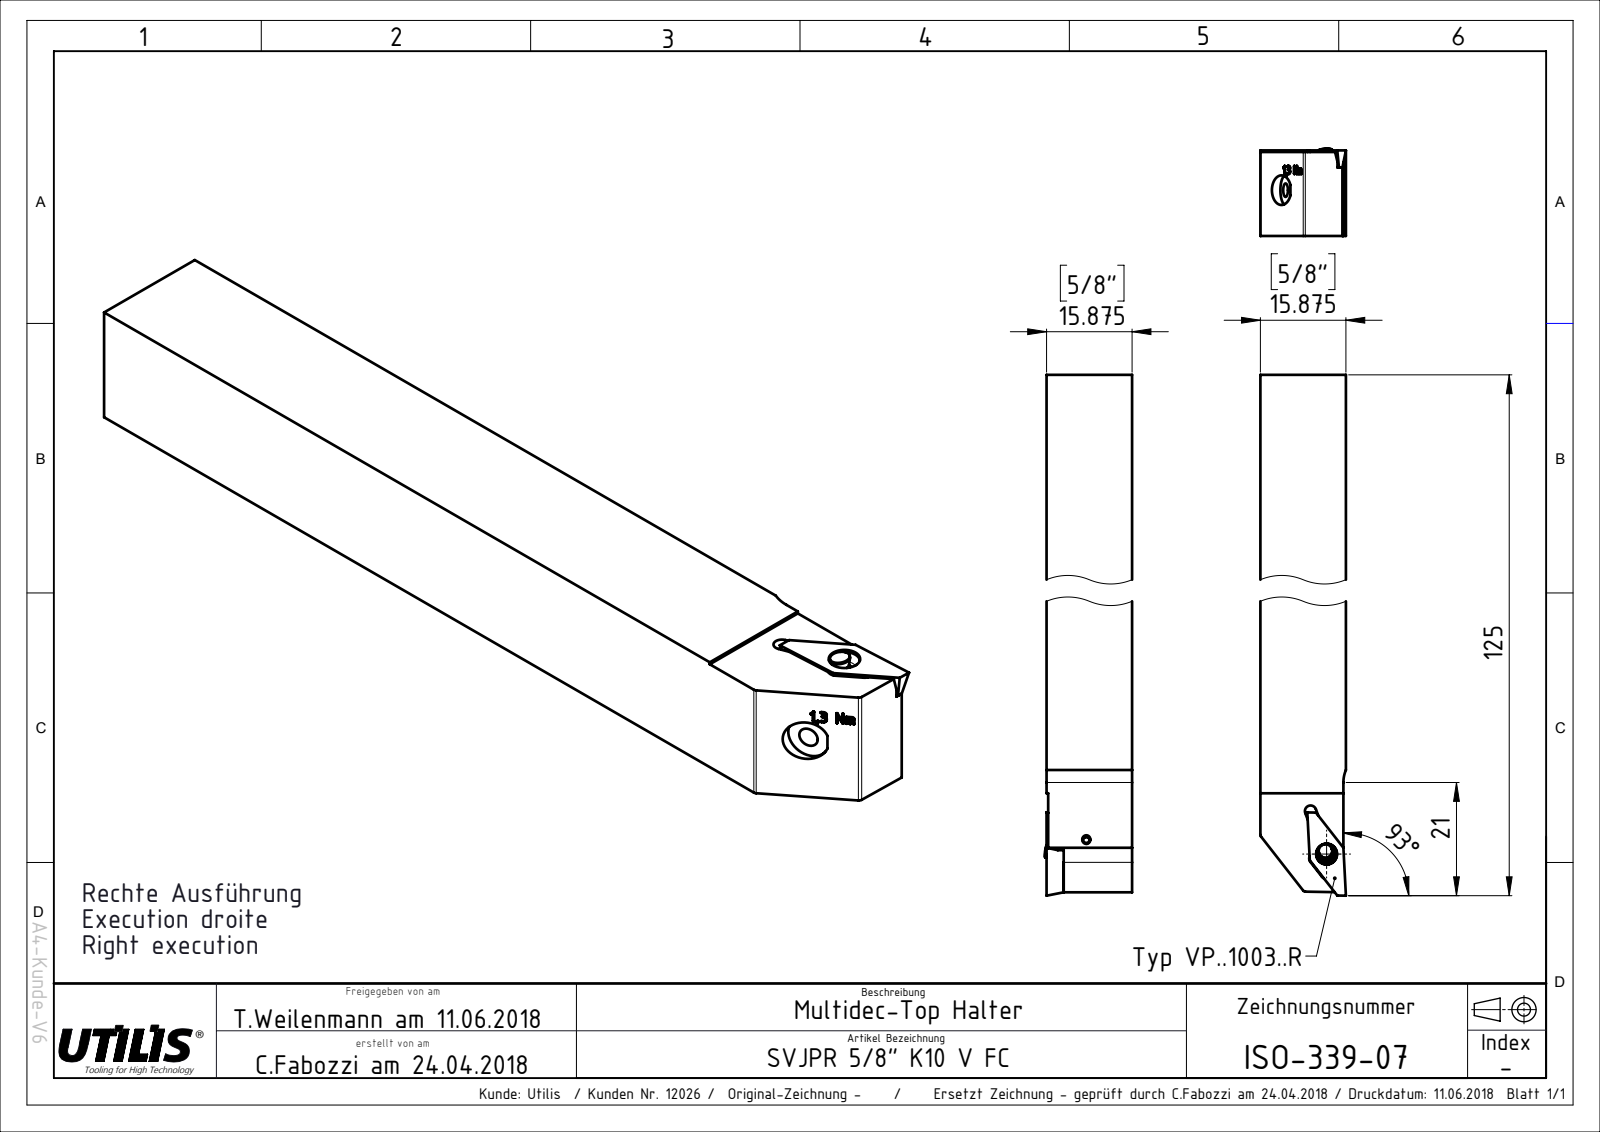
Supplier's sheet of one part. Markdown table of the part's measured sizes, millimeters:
| quantity | value |
| --- | --- |
| part name | ISO-339-07 |
| STEP written by | SolidWorks 2018 (AUTOMOTIVE_DESIGN) |
| units | millimeters |
| bodies | 1 solid, 110 faces (58 planar, 8 cylindrical, 44 other) |
| overall size | 125 × 15.88 × 15.88 |
| volume | 30 383 mm³ |
| surface area | 8 316 mm² |
| partial cylindrical surfaces (radius × count) | 1.05 × 3, 0.5 × 2, 6 × 1, 6.1 × 1 |
| main face-to-face distances | 15.88, 15.41, 0.47, 15.58, 3.18, 2.88, 12.7, 4.32, 10.36, 6.04 |
